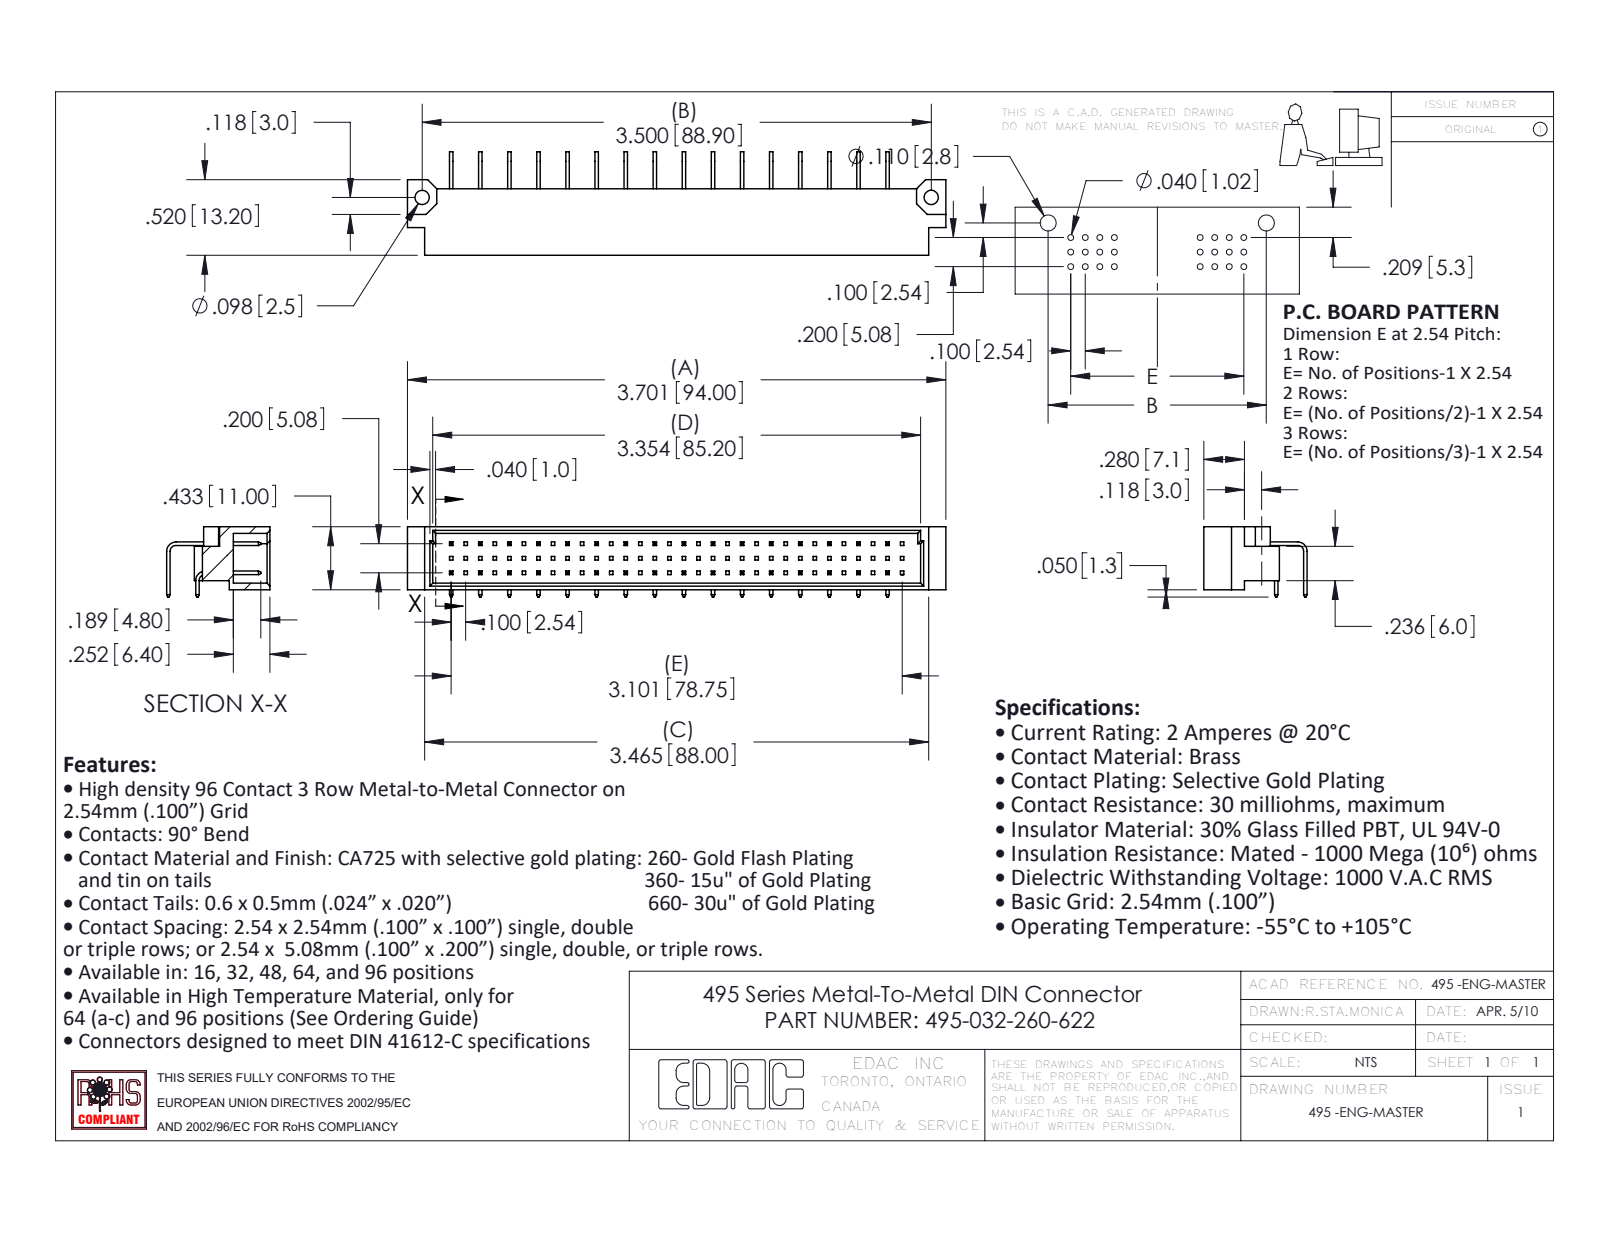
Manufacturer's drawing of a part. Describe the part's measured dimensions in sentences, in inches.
The part is named "495-290-1; 495 Part_96; 495-290-3; 495-032-260-622". Its 3-D file was written by "SolidWorks 2020 (AUTOMOTIVE_DESIGN)". It is 33 solids with 1009 faces: 941 planar, 68 cylindrical and 0 other. Overall it measures 3.701 by 0.711 by 0.483 inches. Its volume is 0.376 cubic inches and its surface area 12.99 square inches. Round holes: 2 of diameter 0.098. Partial cylindrical surfaces (rounded edges, fillets, slot ends): 2 of radius 0.04, 2 of radius 0.065. The main face-to-face distances are 0.045, 0.388, 0.2, 0.205, 0.433, 0.024, 0.343, 0.063, 0.37, 0.018. The hole center spacings are 3.5.
